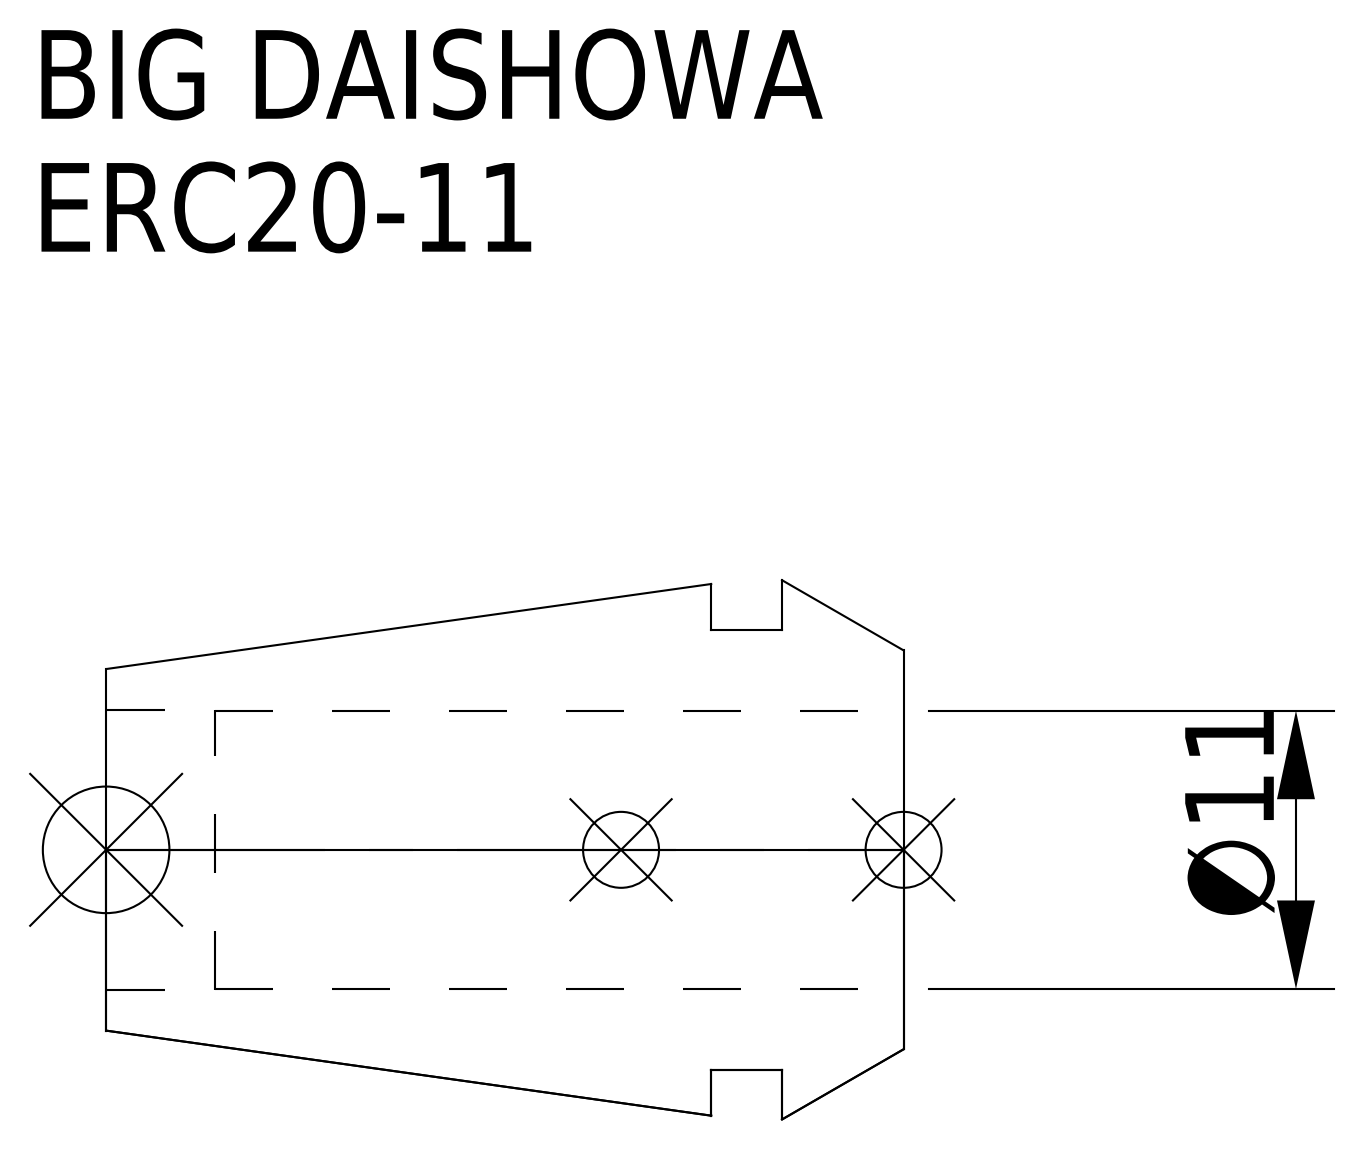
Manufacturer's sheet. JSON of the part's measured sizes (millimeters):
{"part_name": "ERC20-11", "step_written_by": "CREO PARAMETRIC BY PTC INC, 2016380 (AUTOMOTIVE_DESIGN)", "units": "millimeters", "bodies": {"solids": 1, "faces": 15, "planar": 5, "cylindrical": 6, "other": 4}, "overall_size": [31.5, 21.3, 21.3], "volume_mm3": 4885, "surface_area_mm2": 3295, "round_holes": [[11, 1], [11.05, 1]], "round_bosses_or_shafts": [[17.4, 1]], "face_to_face_distances": [2.8, 4.8, 7.6, 31.5, 26.7, 23.9, 27.2, 22.4, 19.6, 4.3]}
